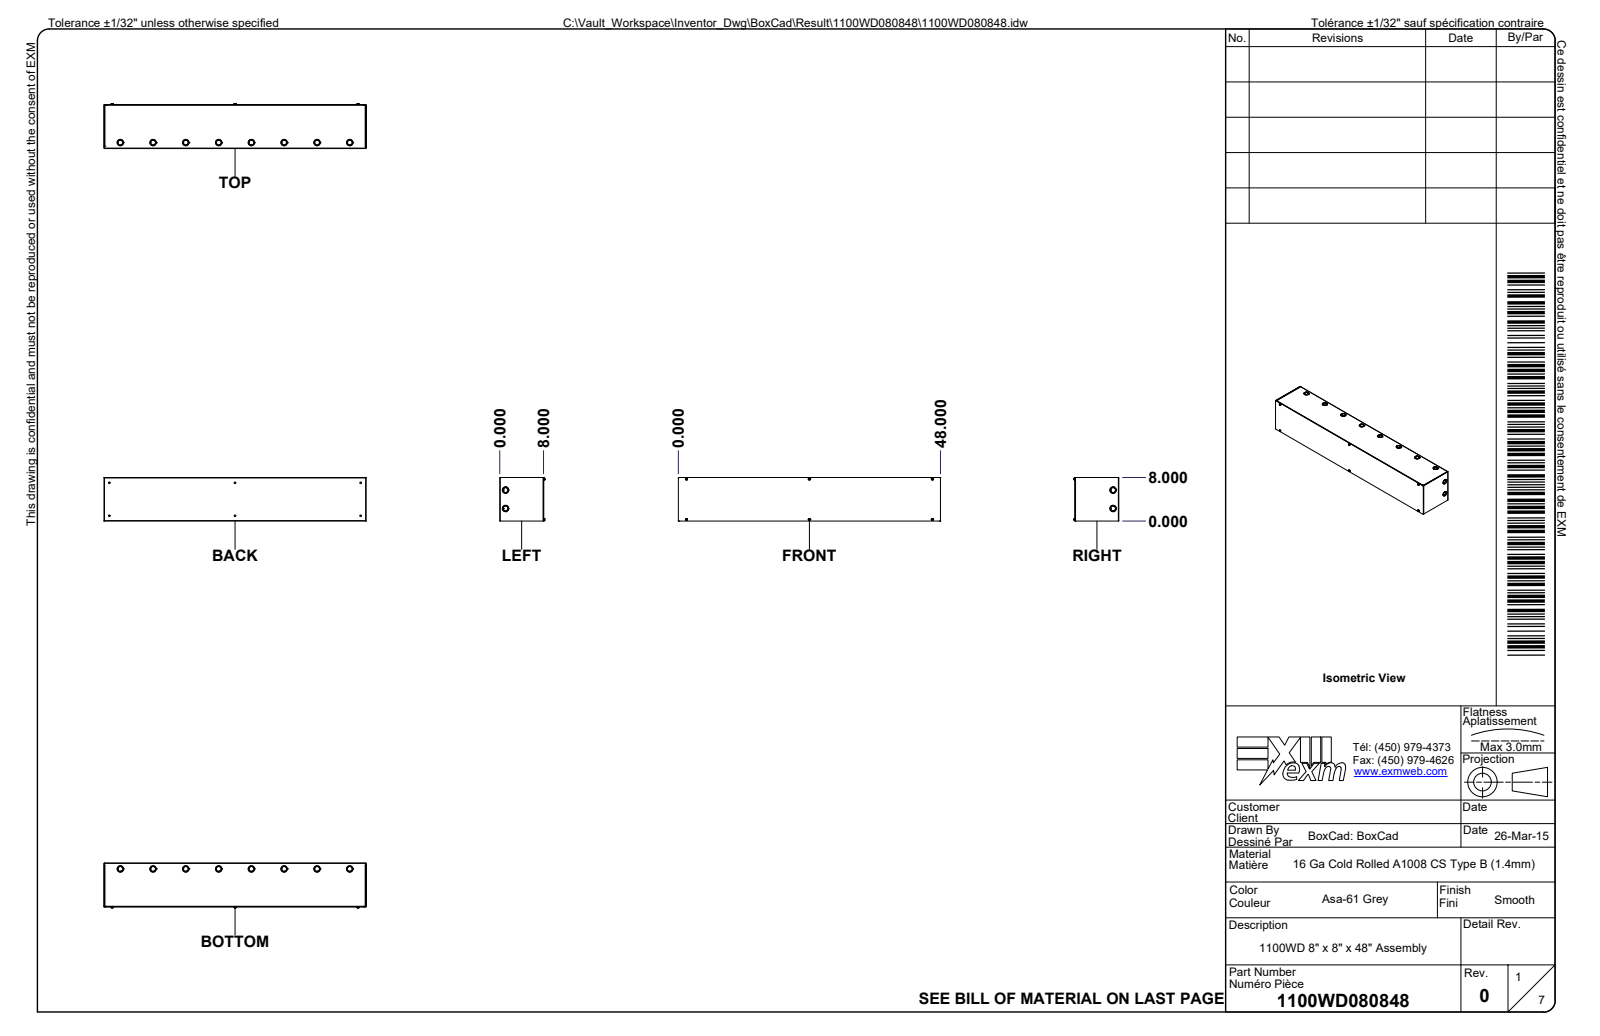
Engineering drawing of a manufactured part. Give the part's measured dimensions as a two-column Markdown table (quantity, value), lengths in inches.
| quantity | value |
| --- | --- |
| part name | 1100WD080848; 1100WD080848B; 1100WD080848B-P; 1100WD080848C (+5 more) |
| STEP written by | Autodesk Inventor 2024 (AUTOMOTIVE_DESIGN) |
| units | inches |
| bodies | 10 solids, 4053 faces (2376 planar, 645 cylindrical, 1032 other) |
| overall size | 48 × 8.183 × 8 |
| volume | 93.62 in³ |
| surface area | 3 466 in² |
| round holes (diameter × count) | 0.29 × 12, 0.875 × 10, 1.125 × 10, 0.165 × 6, 0.033 × 2, 0.177 × 2, 0.043 × 1, 0.312 × 1, 1.063 × 1 |
| round bosses / shafts (diameter × count) | 1.125 × 10, 0.875 × 10, 0.374 × 6, 0.03 × 2, 1.25 × 1, 1.142 × 1, 0.25 × 1, 0.051 × 1 |
| partial cylindrical surfaces (radius × count) | 0.004 × 42, 0.059 × 18, 0.11 × 18, 0.031 × 14, 0.086 × 14, 0.062 × 4, 0.094 × 4, 0.125 × 4 |
| main face-to-face distances | 0.055, 7.945, 8, 7.89, 0.053, 8.053, 7.998, 47.945, 48, 47.89 |
| hole center spacings | 6, 12, 18, 0.86, 6.719, 22.5, 22.511, 23 |
